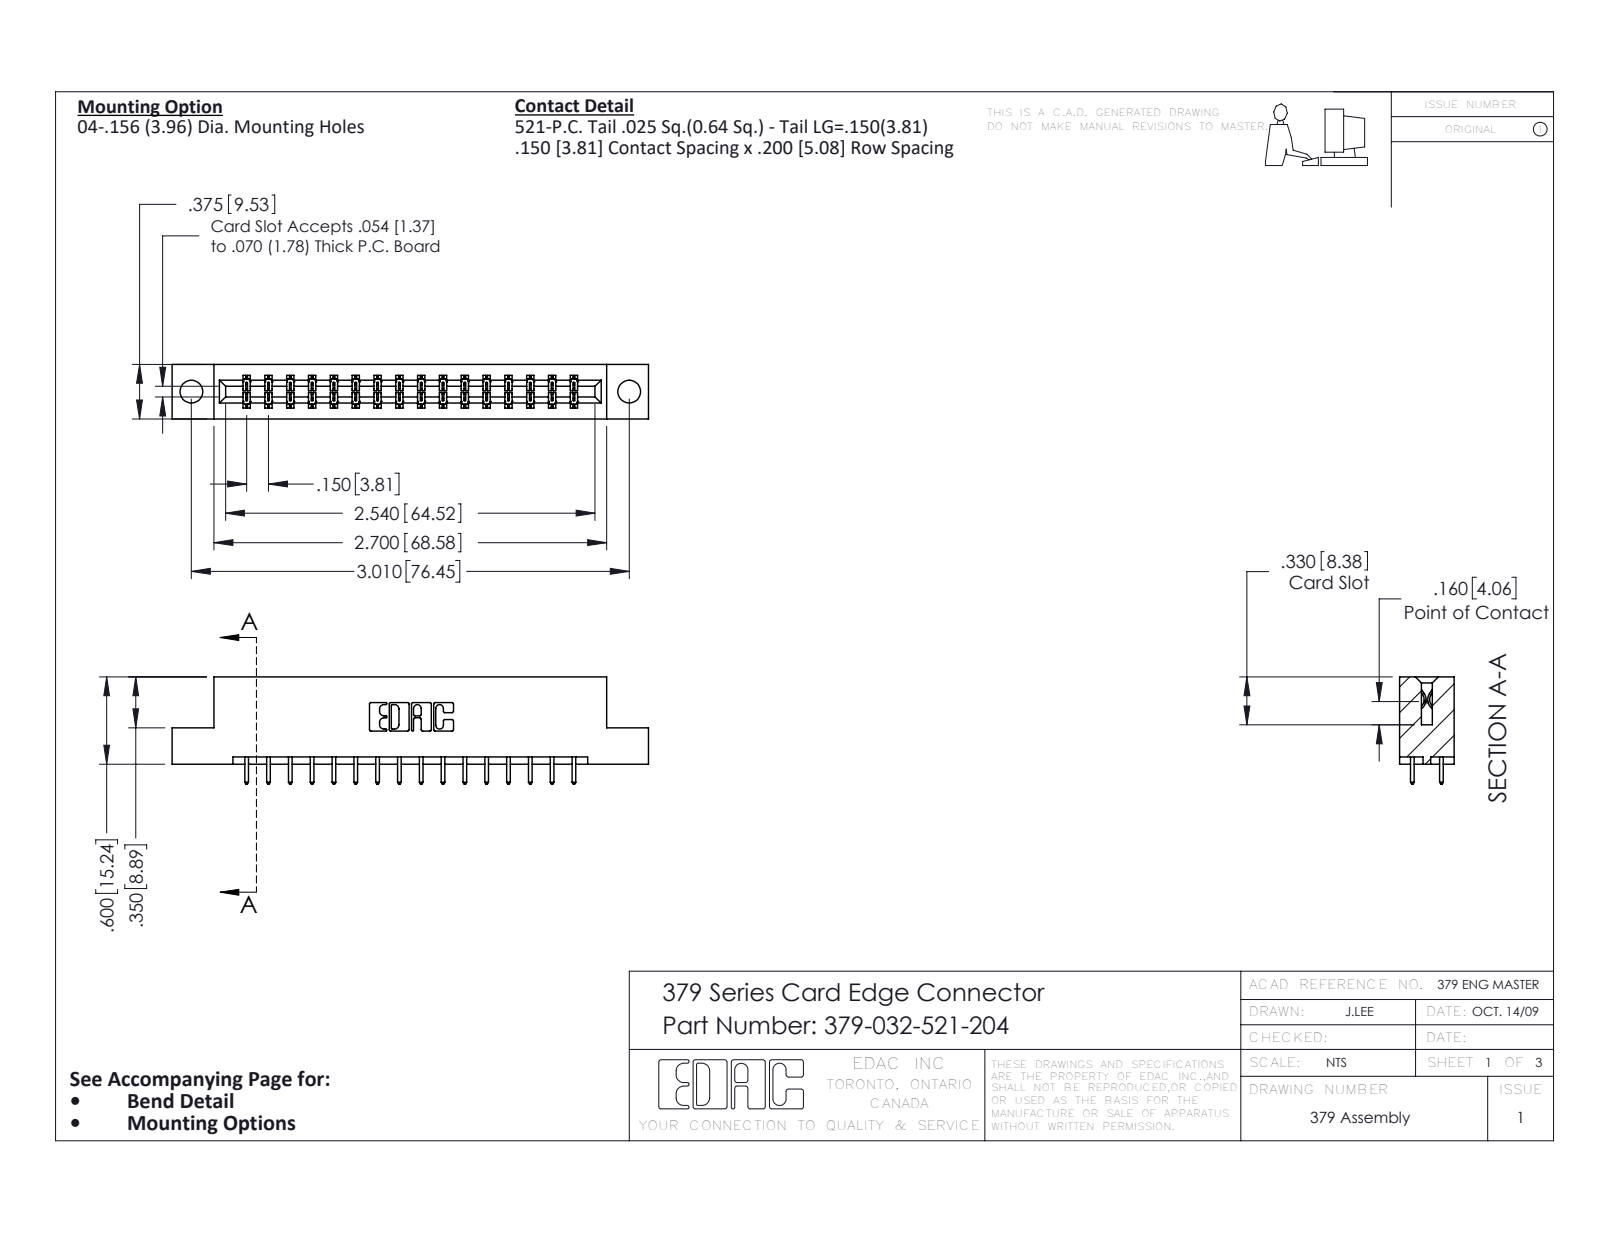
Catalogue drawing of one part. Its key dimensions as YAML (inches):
part_name: "379 Part_Flush - .156 Dia - TH; 345-292-001_345-293-121; 379-032-521-204"
step_written_by: "SolidWorks 2020 (CONFIG_CONTROL_DESIGN)"
units: inches
bodies: {solids: 33, faces: 1778, planar: 1222, cylindrical: 556, other: 0}
overall_size: [3.275, 0.737, 0.375]
volume: 0.515
surface_area: 13.85
round_holes:
  - {diameter: 0.156, count: 2}
partial_cylinders:
  - {radius: 0.006, count: 63}
  - {radius: 0.01, count: 32}
  - {radius: 0.01, count: 22}
  - {radius: 0.007, count: 6}
  - {radius: 0.031, count: 6}
  - {radius: 0.026, count: 3}
  - {radius: 0.014, count: 2}
  - {radius: 0.022, count: 2}
face_to_face_distances: [0.3, 0.075, 0.375, 0.2, 0.1, 0.15, 0.05, 0.6, 0.225, 0.55]
hole_center_spacings: [3.01]
